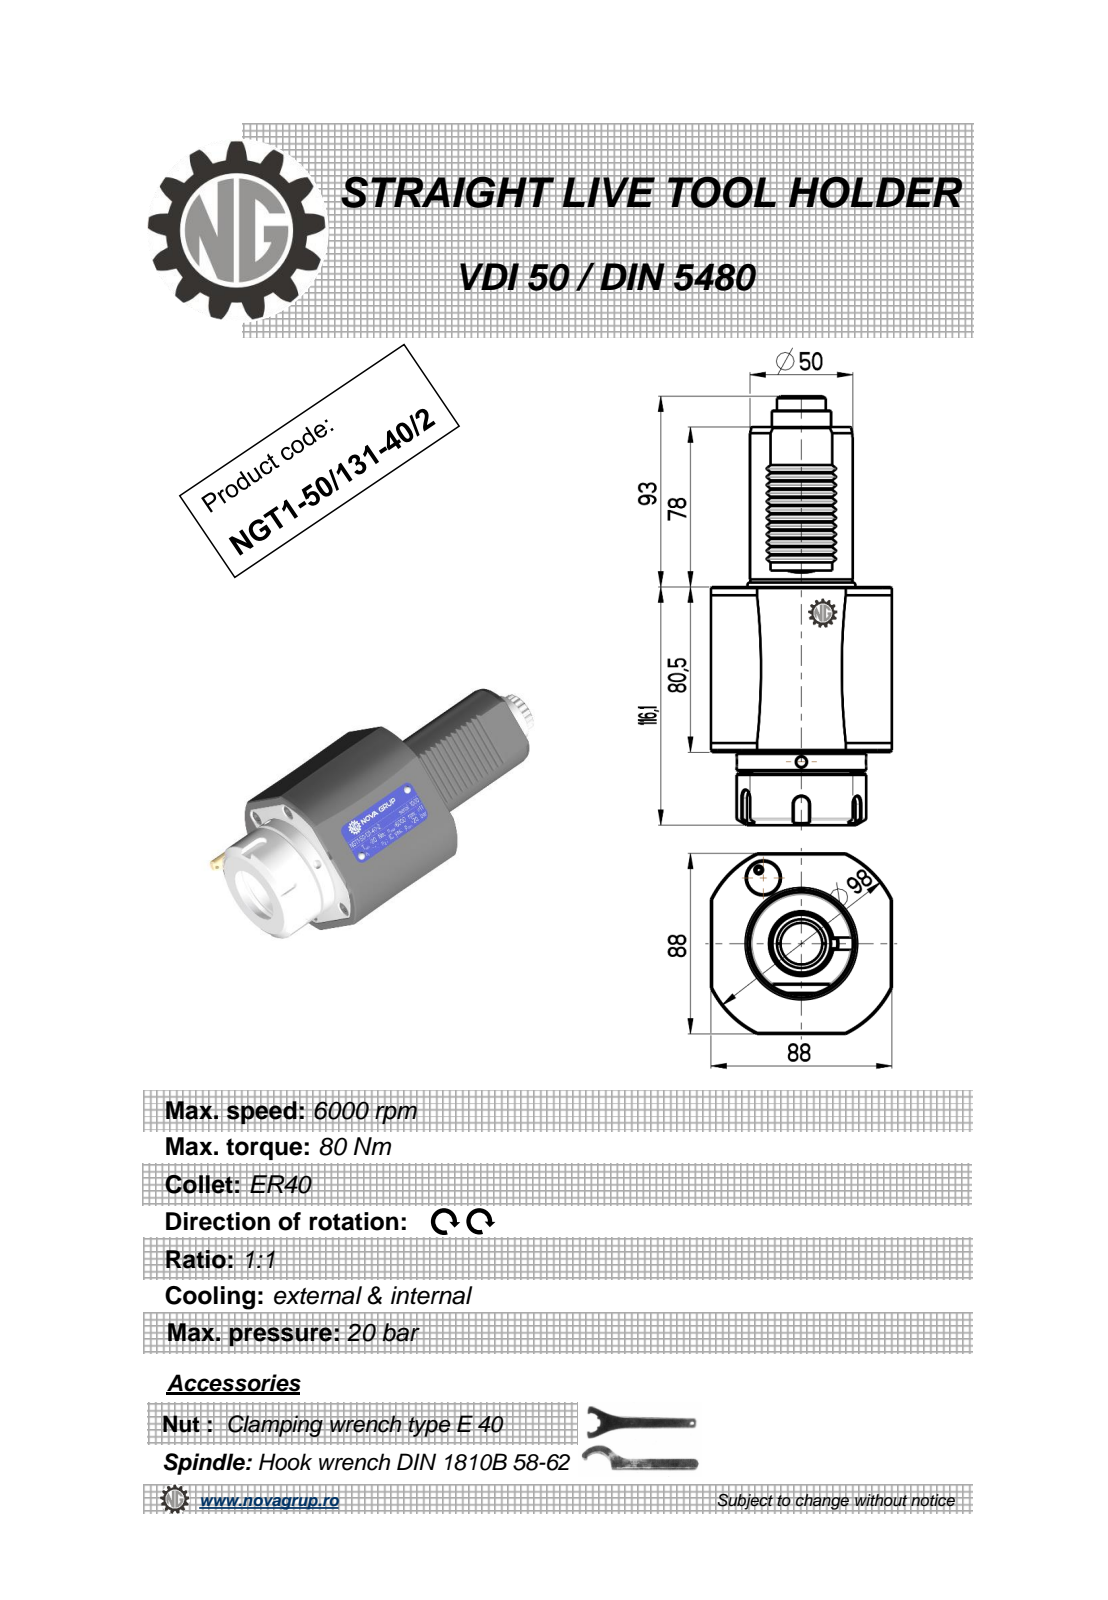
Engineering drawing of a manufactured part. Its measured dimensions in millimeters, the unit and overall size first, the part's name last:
Units: millimetres
Overall size (bounding box): 209.1 × 89.6 × 88
Round holes (diameter × count): ⌀5 ×2, ⌀2.5 ×1, ⌀3 ×1, ⌀33.5 ×1
Round bosses / shafts (diameter × count): ⌀63 ×1, ⌀51 ×1, ⌀50 ×1, ⌀28.8 ×1, ⌀9 ×1, ⌀7 ×1, ⌀5 ×1
Partial cylindrical surfaces — rounded edges, fillets, slot ends (radius × count): R3.04 ×36, R0.3 ×12, R3.75 ×5, R10.56 ×1, R11.88 ×1, R17.5 ×1, R49 ×1
Main face-to-face distances: 88, 80.5, 116.1, 35.6, 109.9, 29.4, 6.2, 2.83, 9, 78
Hole centre spacings: 41.5
Volume: 807 656 mm³ · Surface area: 65 868 mm²
Bodies: 1 solid, 371 faces (111 planar, 134 cylindrical, 126 other)
Part name (STEP PRODUCT): NGT1_50_131_40_1
STEP written by: PRO/ENGINEER BY PARAMETRIC TECHNOLOGY CORPORATION, 2010280 (CONFIG_CONTROL_DESIGN)
